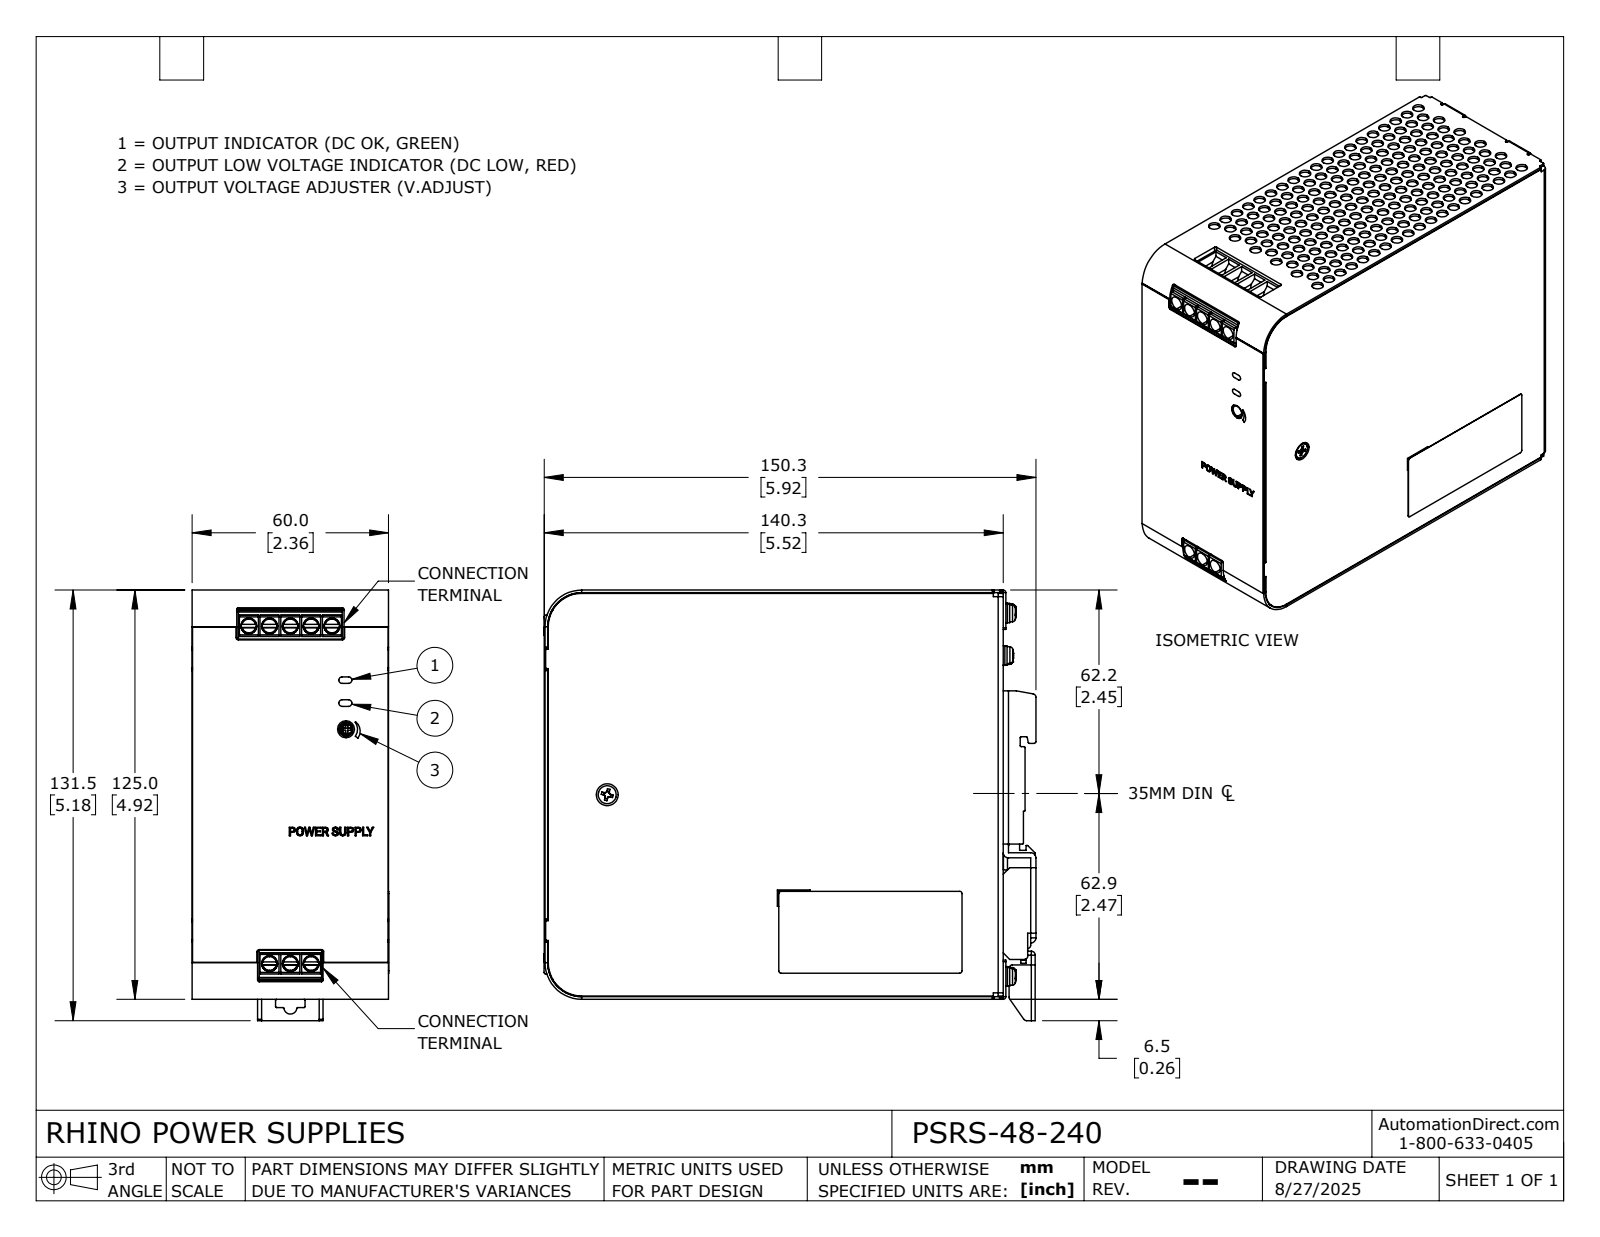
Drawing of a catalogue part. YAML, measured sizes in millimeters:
part_name: "PSRS-48-240"
step_written_by: "SolidWorks 2024 (AUTOMOTIVE_DESIGN)"
units: millimeters
bodies: {solids: 2, faces: 3059, planar: 1489, cylindrical: 1291, other: 279}
overall_size: [150.3, 131.5, 60.05]
volume: 1048000
surface_area: 95151
round_holes:
  - {diameter: 4, count: 210}
  - {diameter: 3.1, count: 10}
  - {diameter: 3.5, count: 10}
  - {diameter: 4.65, count: 8}
  - {diameter: 4.85, count: 8}
  - {diameter: 3.8, count: 6}
  - {diameter: 3.6, count: 5}
  - {diameter: 2.5, count: 4}
  - {diameter: 6.7, count: 4}
  - {diameter: 1.5, count: 1}
  - {diameter: 3.4, count: 1}
  - {diameter: 4.2, count: 1}
round_bosses_or_shafts:
  - {diameter: 3, count: 16}
  - {diameter: 6, count: 10}
  - {diameter: 5.9, count: 10}
  - {diameter: 4.75, count: 8}
  - {diameter: 5.5, count: 4}
partial_cylinders:
  - {radius: 0.3, count: 61}
  - {radius: 0.5, count: 37}
  - {radius: 0.15, count: 14}
  - {radius: 1, count: 14}
  - {radius: 1.6, count: 13}
  - {radius: 1.2, count: 9}
  - {radius: 0.1, count: 7}
  - {radius: 0.6, count: 2}
face_to_face_distances: [60, 0.8, 124.2, 140.25, 125, 1.6, 123.4, 8.4, 13.6, 1.2]
hole_center_spacings: [11.64, 5.6, 15.15, 11.2, 21.15, 19.65, 10.2, 23.27]
